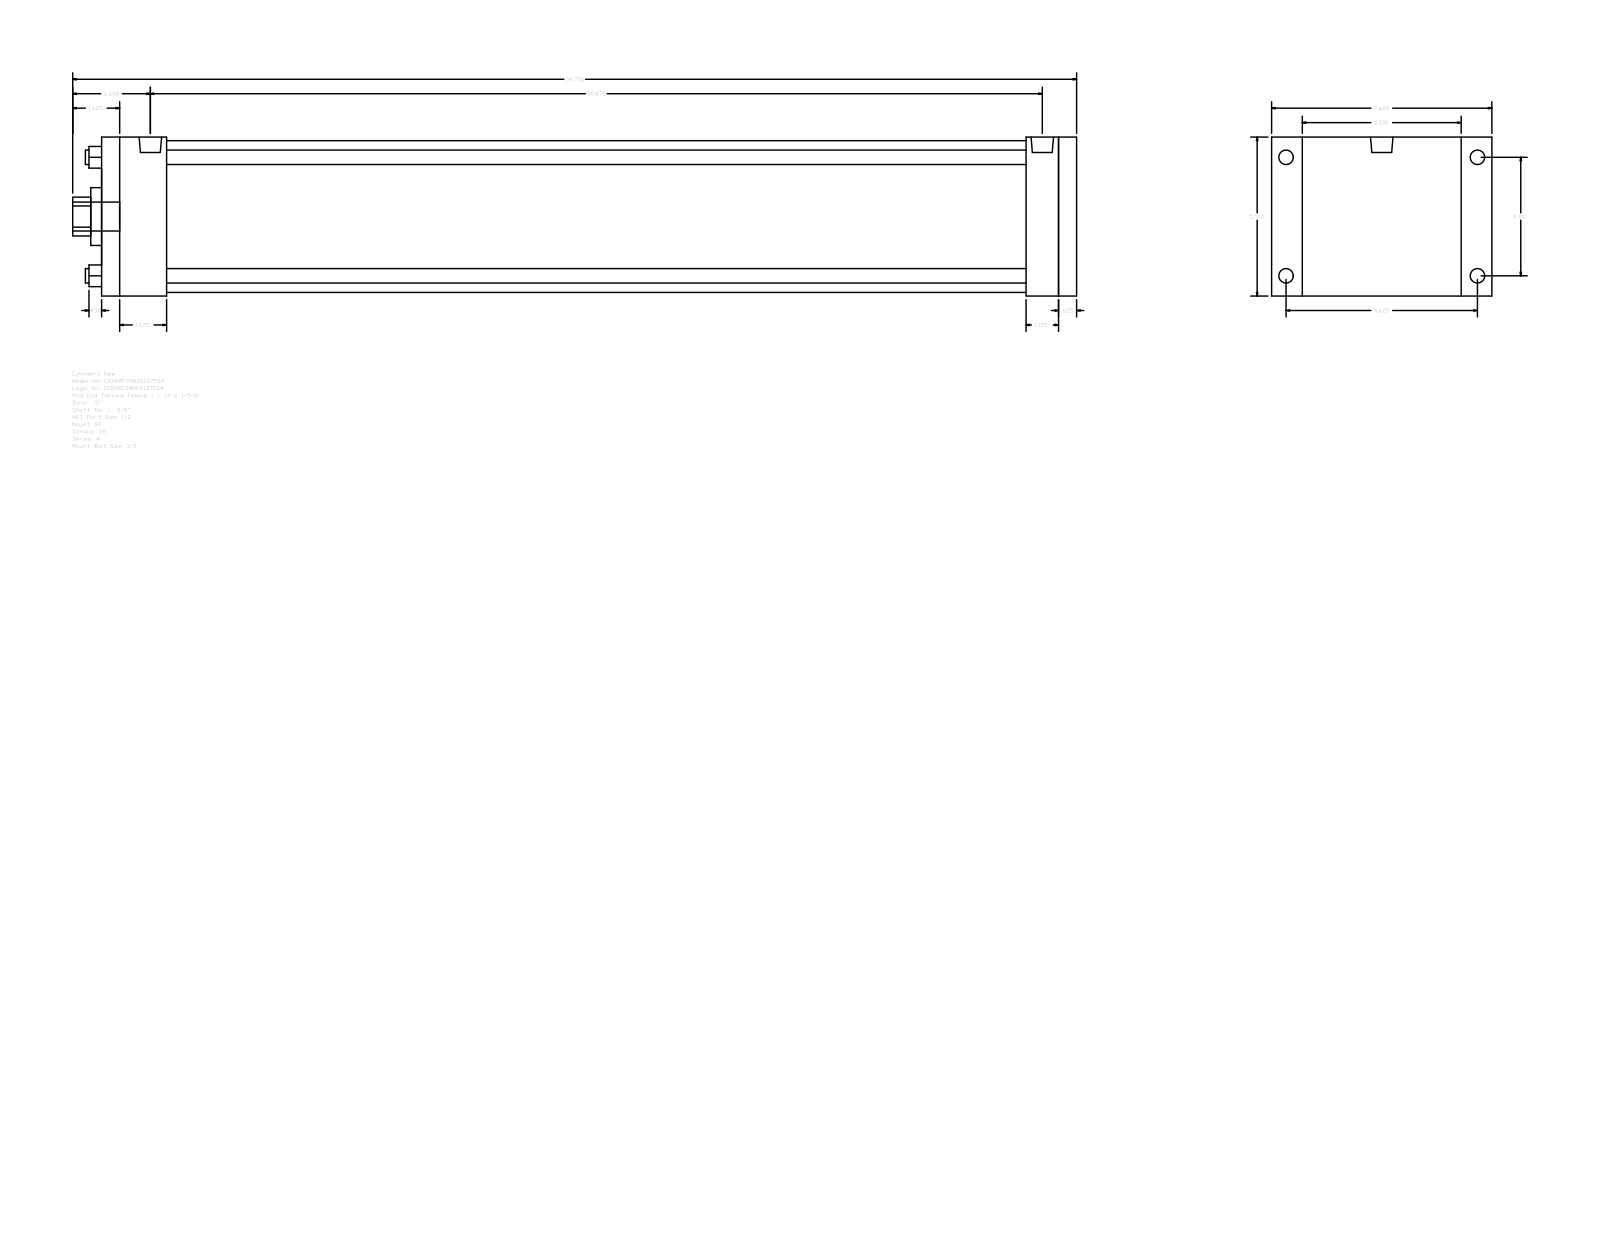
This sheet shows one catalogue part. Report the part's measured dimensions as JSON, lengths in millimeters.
{"part_name": "A_RF__0500_1.375", "step_written_by": "GSSL Pune (CONFIG_CONTROL_DESIGN)", "units": "millimeters", "bodies": {"solids": 0, "faces": 92, "planar": 64, "cylindrical": 28, "other": 0}, "overall_size": [882.65, 193.68, 139.7], "round_holes": [[12.7, 4], [34.92, 1], [50.8, 1], [133.35, 1]], "round_bosses_or_shafts": [[12.7, 4], [8.73, 4], [19.77, 2], [25.4, 1]], "partial_cylinders_radius": [[17.06, 1]], "face_to_face_distances": [139.7, 857.25, 15.88, 841.37, 28.57, 57.15, 784.22, 800.1, 812.8, 755.65], "hole_center_spacings": [73.64, 104.14, 147.28]}
